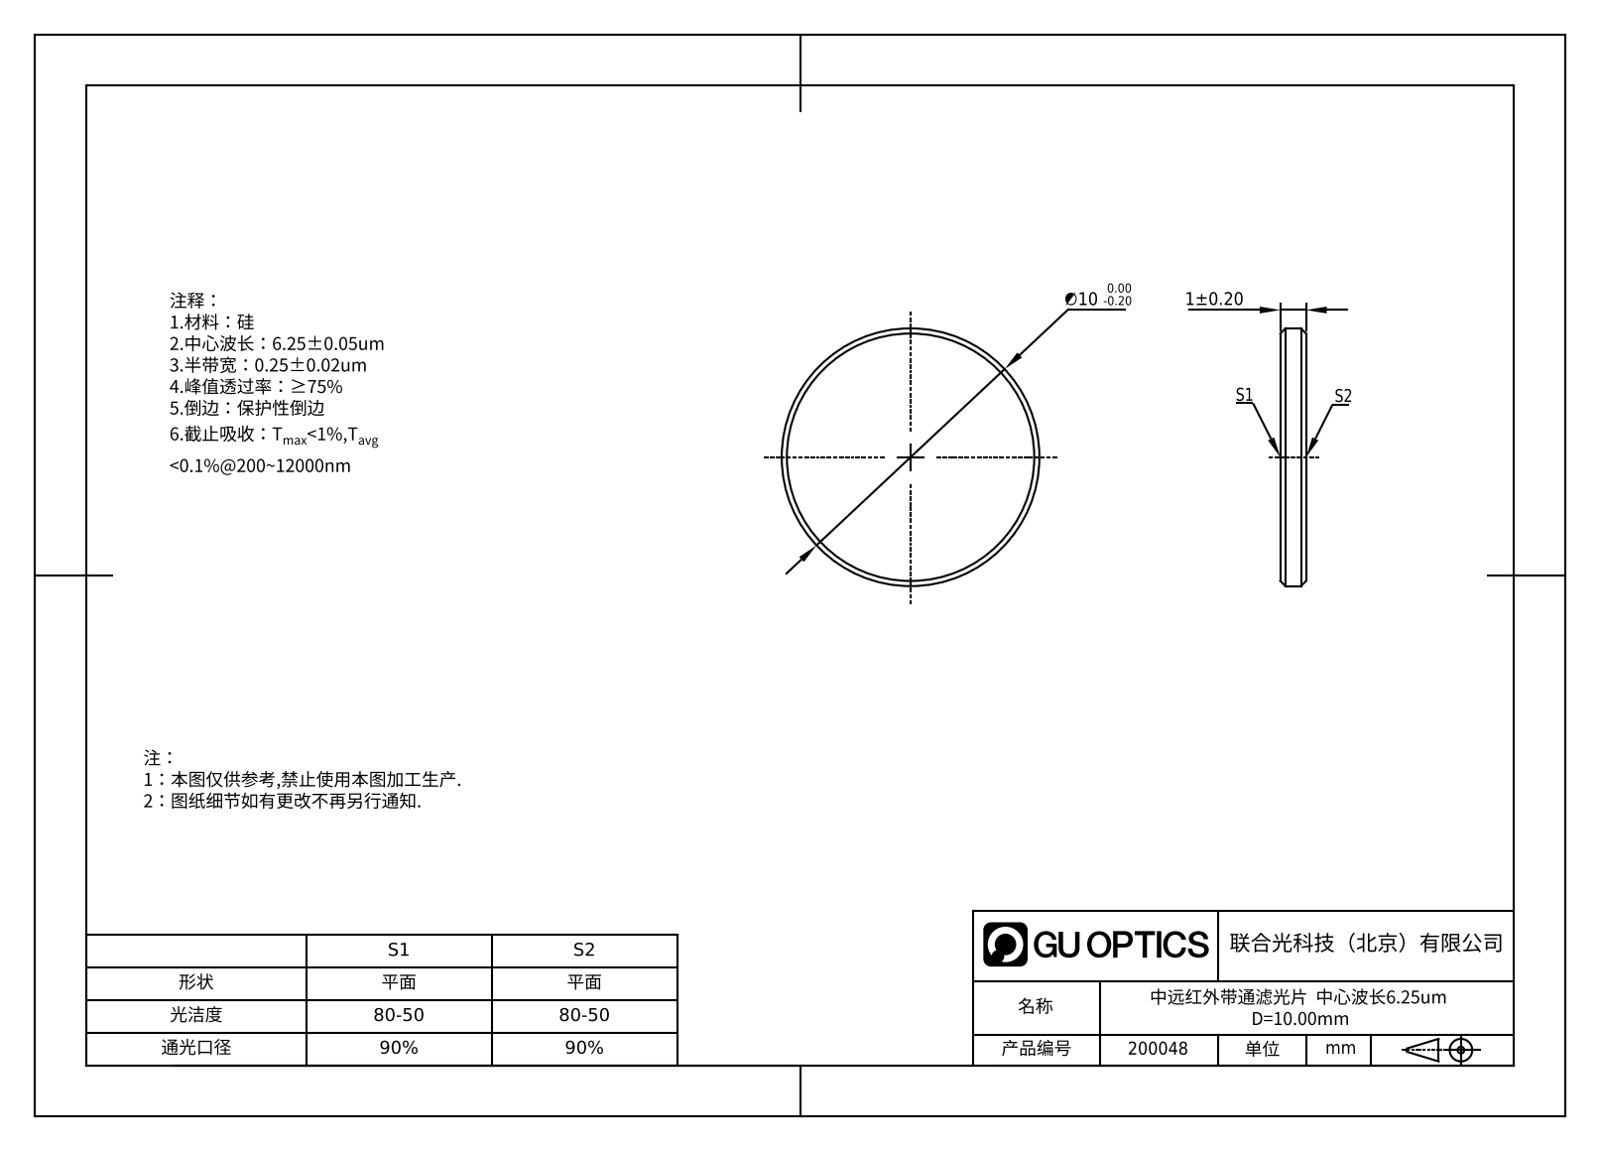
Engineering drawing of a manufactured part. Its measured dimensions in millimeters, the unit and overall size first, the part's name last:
Units: millimetres
Overall size (bounding box): 10 × 10 × 1
Round bosses / shafts (diameter × count): ⌀10 ×1
Main face-to-face distances: 1
Volume: 77 mm³ · Surface area: 181 mm²
Bodies: 1 solid, 8 faces (2 planar, 2 cylindrical, 4 other)
Part name (STEP PRODUCT): GNIF-250-6250-D10
STEP written by: SolidWorks 2022 (AUTOMOTIVE_DESIGN)
